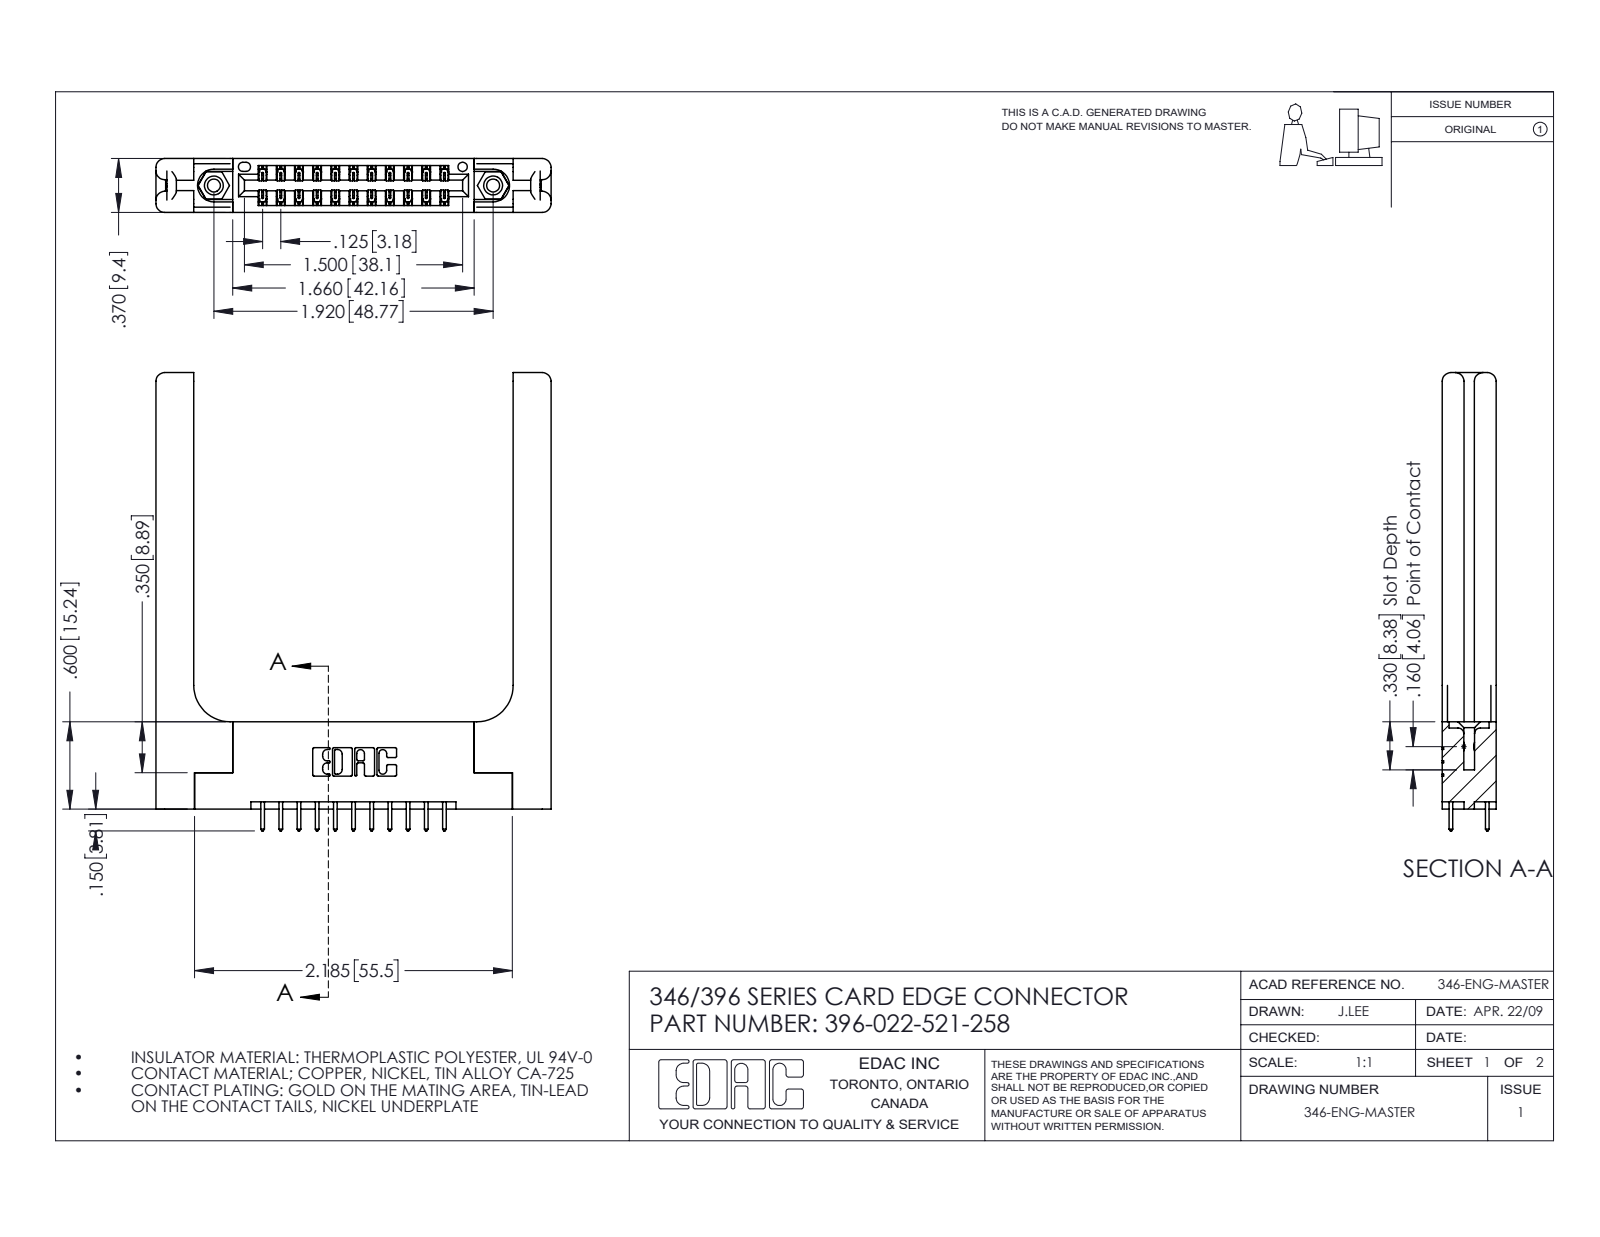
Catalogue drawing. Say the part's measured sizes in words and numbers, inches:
The part is named "346 Part_Flush Mounting Lugs - 0.156 Dia-TH; 346-220-058_345-220-058; 345-250-001_345-250-001-102; 345-292-001_345-293-121 (+1 more)". Its 3-D file was written by "SolidWorks 2016 (CONFIG_CONTROL_DESIGN)". It is 27 solids with 1522 faces: 994 planar, 468 cylindrical and 60 other. Overall it measures 3.15 by 2.716 by 0.37 inches. Its volume is 0.853 cubic inches and its surface area 20.66 square inches. Round holes: 2 of diameter 0.089, 2 of diameter 0.125, 2 of diameter 0.156, 1 of diameter 0.064. Round bosses or shafts: 2 of diameter 0.155. Partial cylindrical surfaces (rounded edges, fillets, slot ends): 33 of radius 0.006, 22 of radius 0.01, 22 of radius 0.01, 16 of radius 0.06, 6 of radius 0.007, 6 of radius 0.031, 3 of radius 0.026, 2 of radius 0.014. The main face-to-face distances are 0.37, 0.15, 0.072, 0.148, 0.048, 0.322, 0.25, 0.102, 0.22, 0.173. The hole center spacings are 0.246, 1.715, 1.92.
